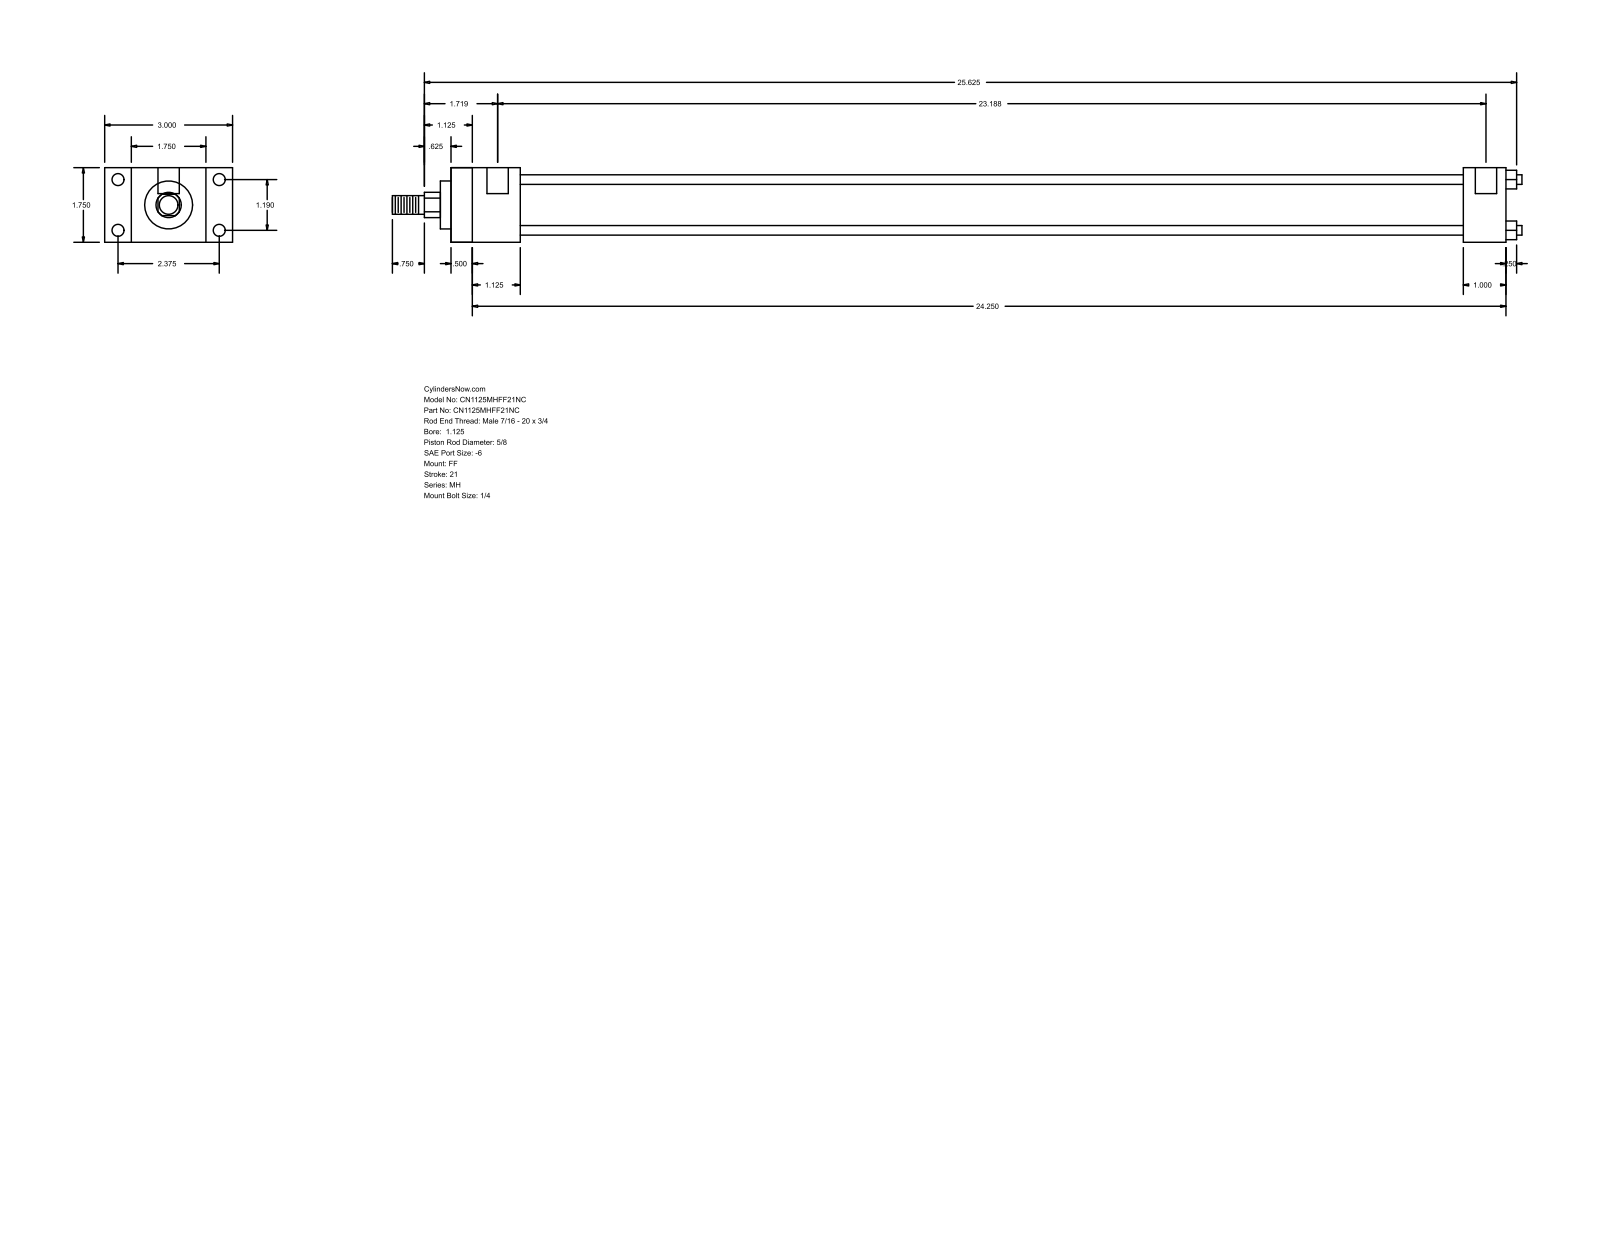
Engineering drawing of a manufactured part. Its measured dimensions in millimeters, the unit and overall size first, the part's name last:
Units: millimetres
Overall size (bounding box): 673.1 × 76.2 × 44.45
Round holes (diameter × count): ⌀5.56 ×4, ⌀7.14 ×4, ⌀12.7 ×2
Round bosses / shafts (diameter × count): ⌀5.71 ×4, ⌀34.92 ×1, ⌀28.57 ×1, ⌀15.88 ×1, ⌀11.11 ×1
Partial cylindrical surfaces — rounded edges, fillets, slot ends (radius × count): R7.54 ×1
Main face-to-face distances: 44.46, 628.64, 15.87, 12.69, 615.95, 28.58, 60.33, 25.4, 41.27, 603.24
Hole centre spacings: 30.22, 60.32, 67.47, 585.79, 3.17, 588.96
Bodies: 0 solids, 92 faces (64 planar, 28 cylindrical, 0 other)
Part name (STEP PRODUCT): MH_FF__0112_0.625
STEP written by: GSSL Pune (CONFIG_CONTROL_DESIGN)
